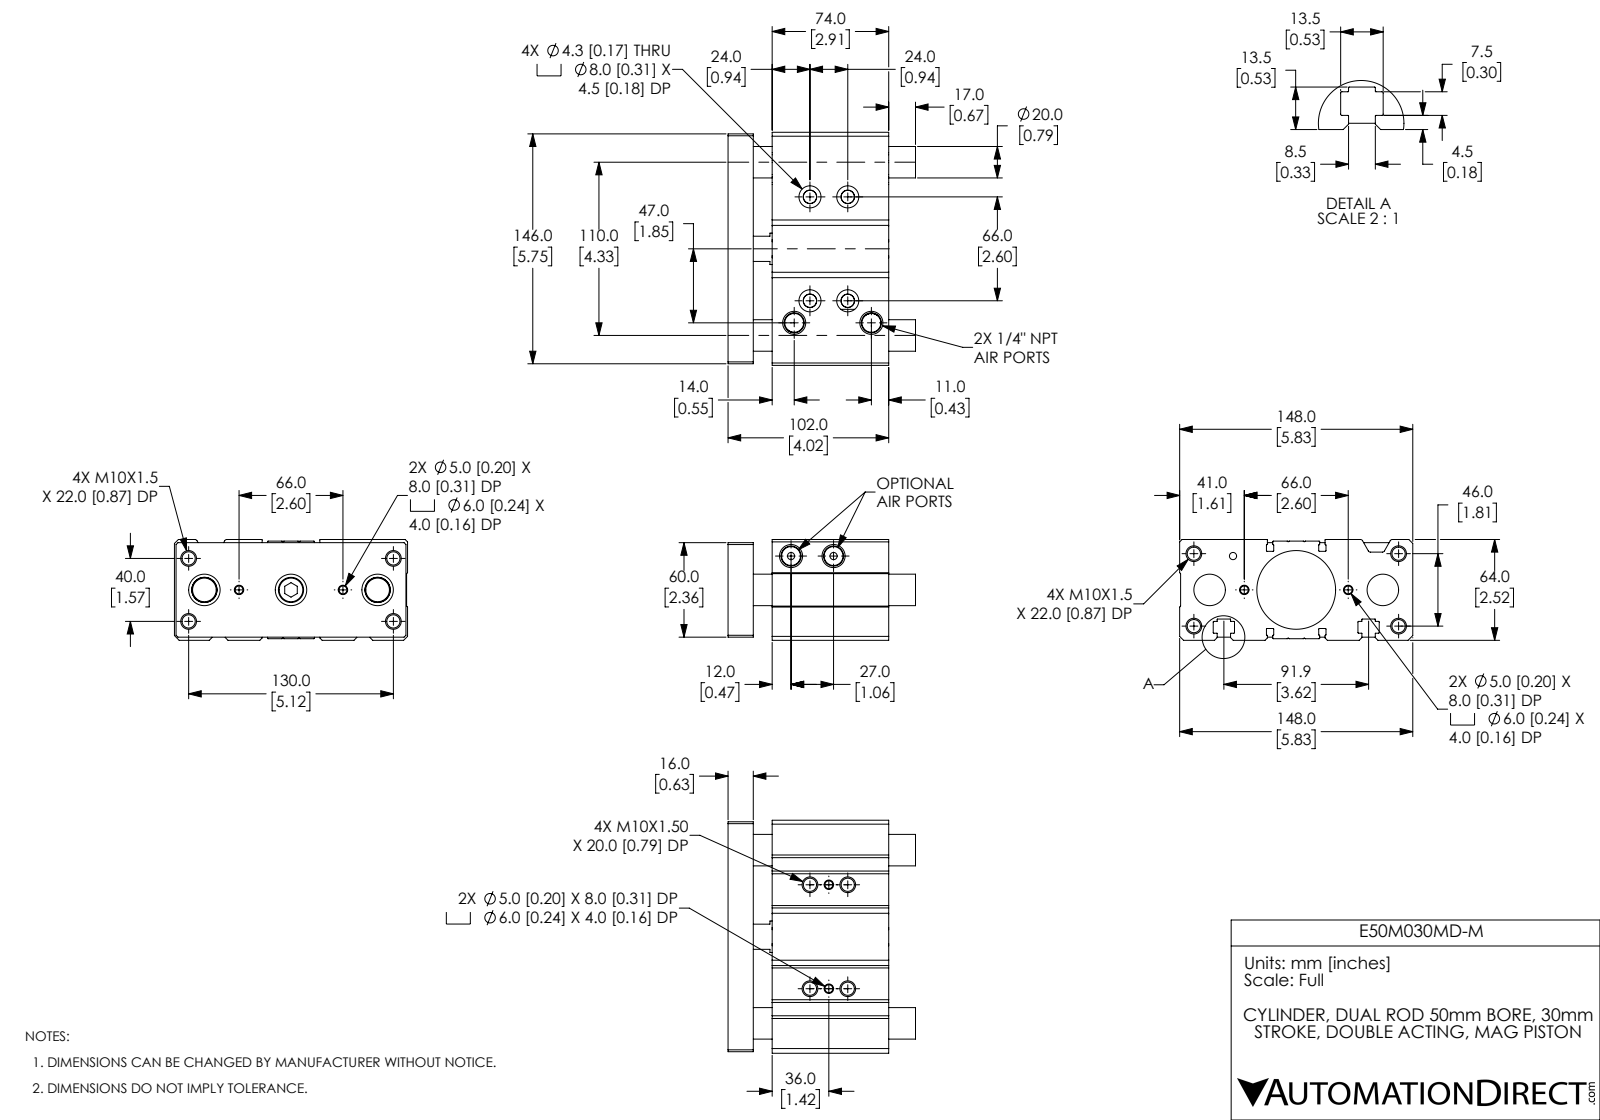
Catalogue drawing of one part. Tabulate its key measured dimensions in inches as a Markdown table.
| quantity | value |
| --- | --- |
| part name | E50M030MD-M_ENDPLATE; E50M030MD-M; E50M030MD-M_BODY |
| STEP written by | SolidWorks 2019 (CONFIG_CONTROL_DESIGN) |
| units | inches |
| bodies | 5 solids, 423 faces (139 planar, 190 cylindrical, 94 other) |
| overall size | 5.827 × 4.685 × 2.52 |
| volume | 44.29 in³ |
| surface area | 232.7 in² |
| round holes (diameter × count) | 0.33 × 12, 0.197 × 4, 0.236 × 4, 0.339 × 4, 0.551 × 4, 0.18 × 3, 0.394 × 3, 0.787 × 3, 0.63 × 2, 0.787 × 1, 1.969 × 1, 1.969 × 1 |
| round bosses / shafts (diameter × count) | 0.63 × 1 |
| partial cylindrical surfaces (radius × count) | 0.008 × 32, 0.016 × 28, 0.059 × 4, 0.012 × 2 |
| main face-to-face distances | 0.039, 0.472, 1.102, 0.63, 2.52, 2.441, 4.016, 3.386, 2.913, 0.217 |
| hole center spacings | 0.118, 0.472, 0.88, 0.987, 1.486, 1.552, 1.693, 2.598 |
